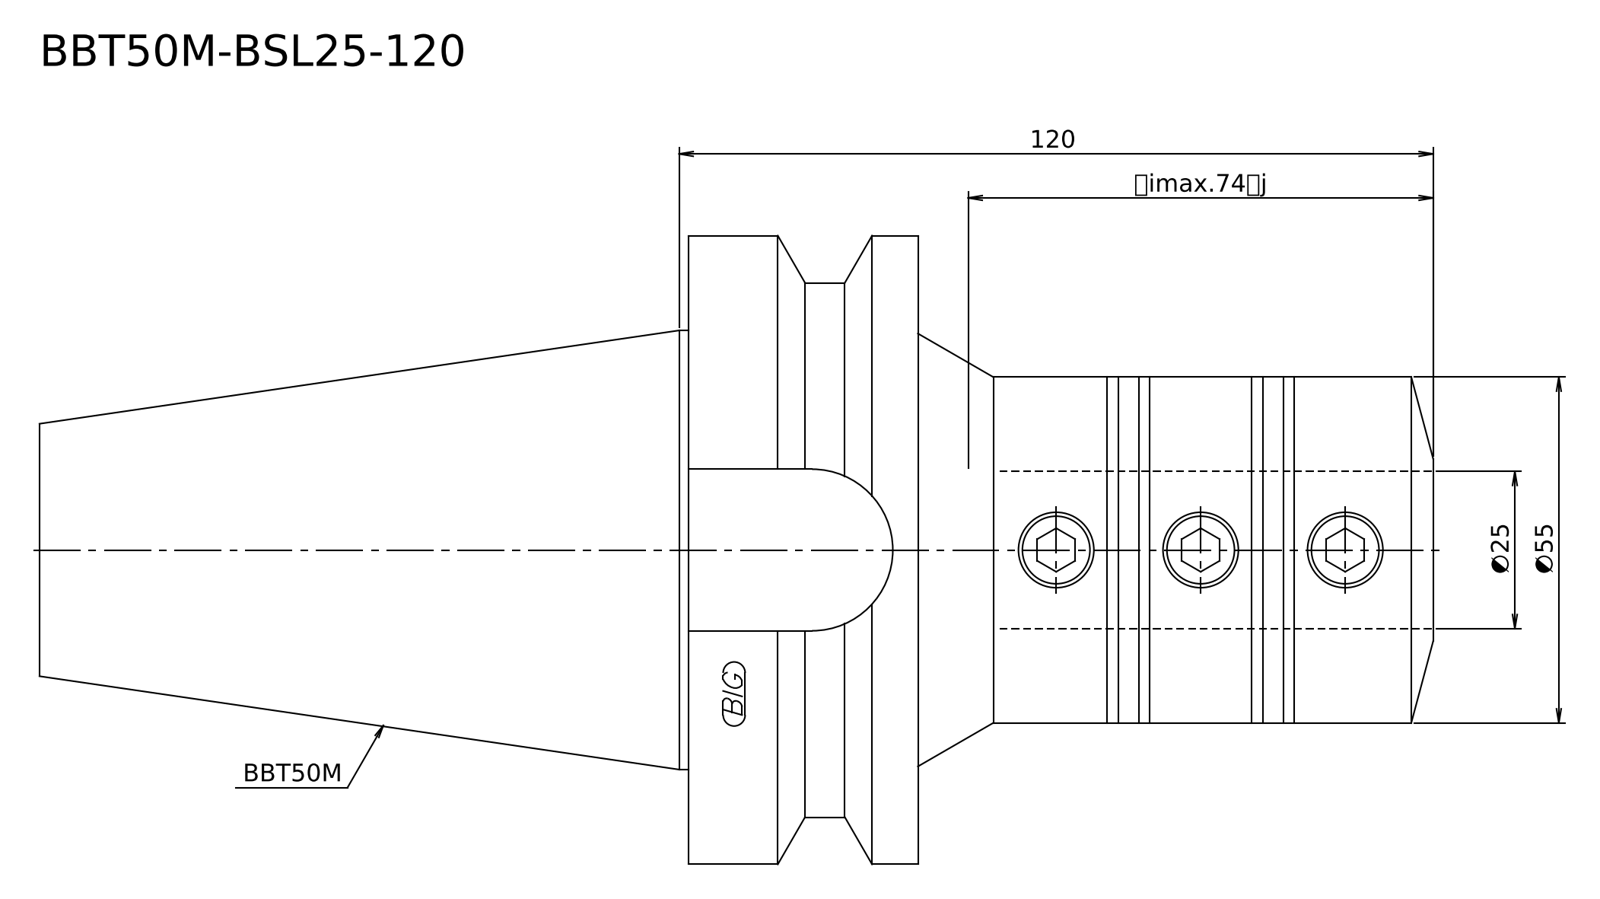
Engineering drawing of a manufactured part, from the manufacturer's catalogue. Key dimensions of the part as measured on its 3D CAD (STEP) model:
STEP written by: Kubotek KeyCreator V8.5.1 (14335) (CONFIG_CONTROL_DESIGN)
Units: millimetres
Bodies: 1 solid, 14 faces (4 planar, 5 cylindrical, 5 other)
Overall size (bounding box): 221.8 × 100 × 100
Volume: 715 987 mm³ · Surface area: 57 631 mm²
Round bosses / shafts (diameter × count): ⌀100 ×1, ⌀85 ×1, ⌀69.85 ×1, ⌀55 ×1
Main face-to-face distances: 36.5, 139.8, 103.3, 82, 118.5, 221.8
